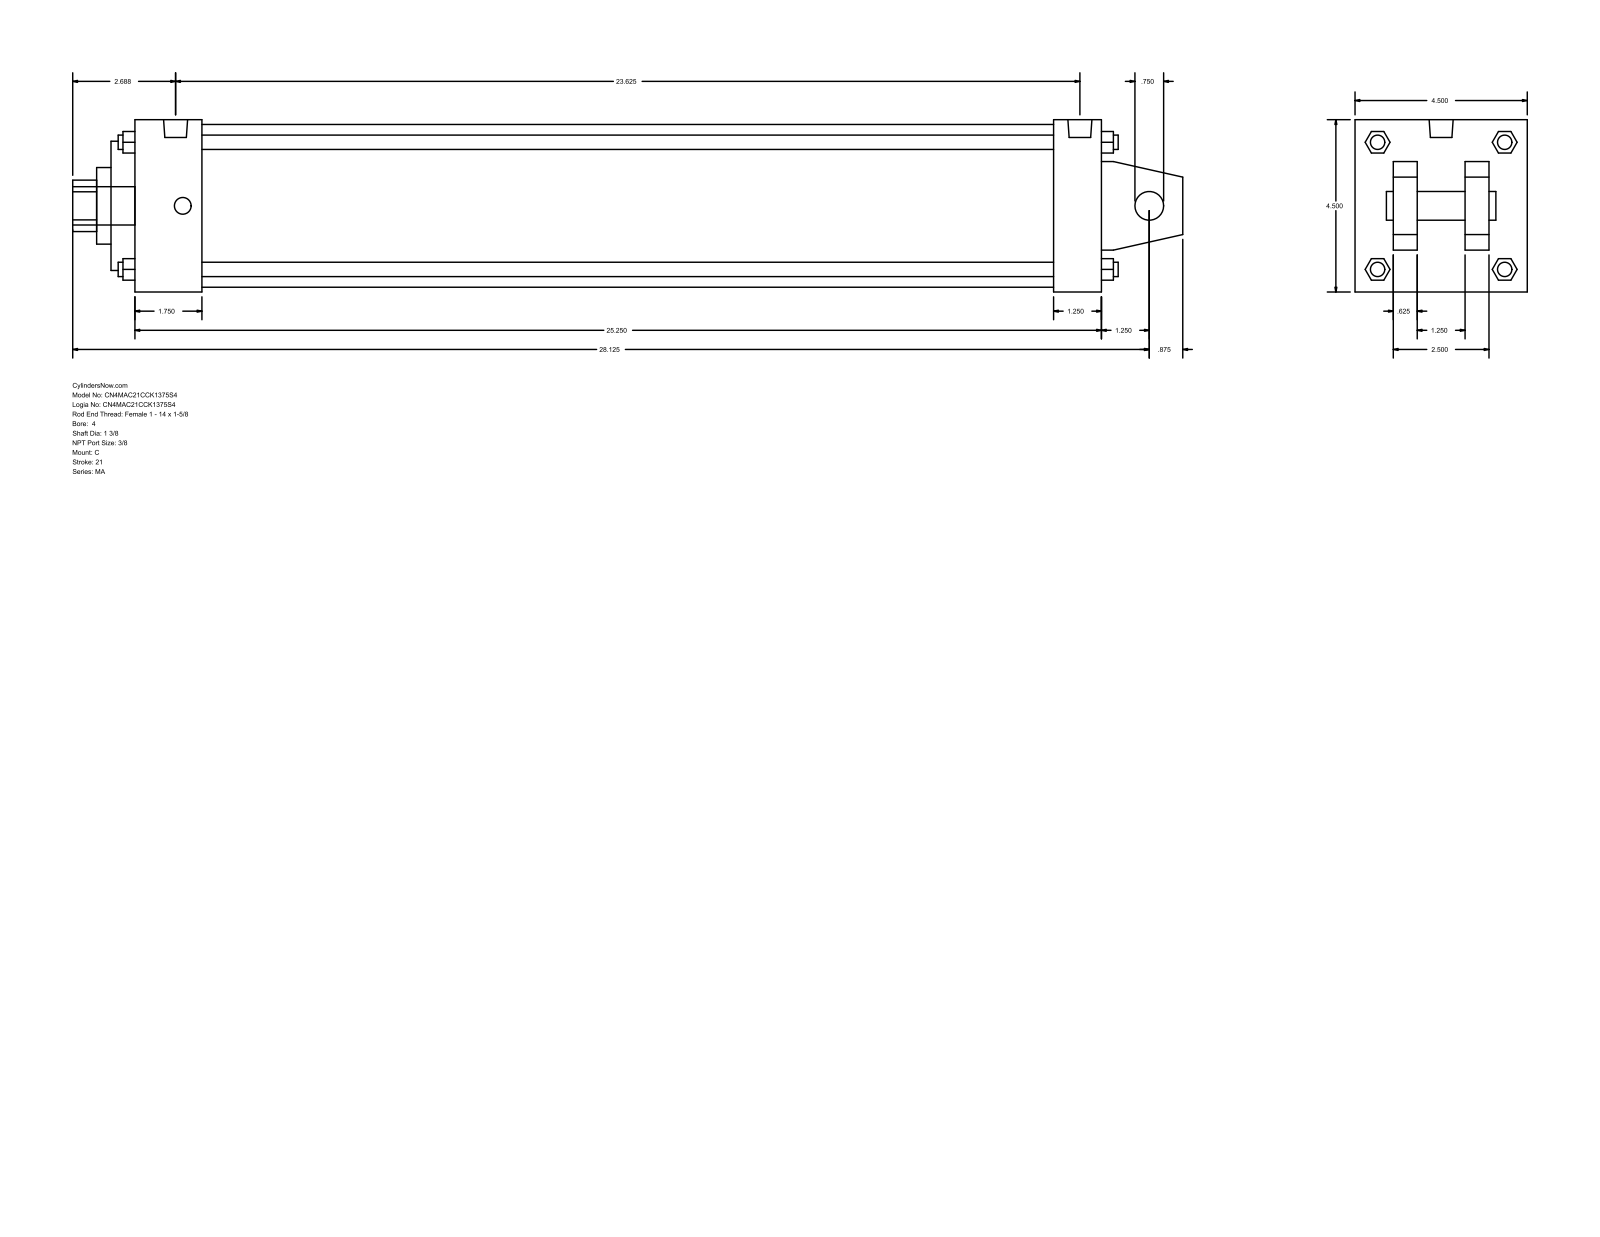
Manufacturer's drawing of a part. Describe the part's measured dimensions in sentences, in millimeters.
The part is named "MA_C__0400_1.375". Its 3-D file was written by "GSSL Pune (CONFIG_CONTROL_DESIGN)". It is 0 solids with 141 faces: 109 planar, 32 cylindrical and 0 other. Overall it measures 736.6 by 114.3 by 114.3 millimeters. Round holes: 1 of diameter 19.05, 1 of diameter 34.92, 1 of diameter 50.8, 1 of diameter 85.72, 1 of diameter 107.95. Round bosses or shafts: 4 of diameter 11.11, 4 of diameter 9.53, 2 of diameter 15.93, 1 of diameter 25.4. Partial cylindrical surfaces (rounded edges, fillets, slot ends): 1 of radius 17.06. The main face-to-face distances are 114.3, 15.87, 641.35, 73.03, 41.27, 25.4, 88.9, 47.63, 657.22, 625.48.
